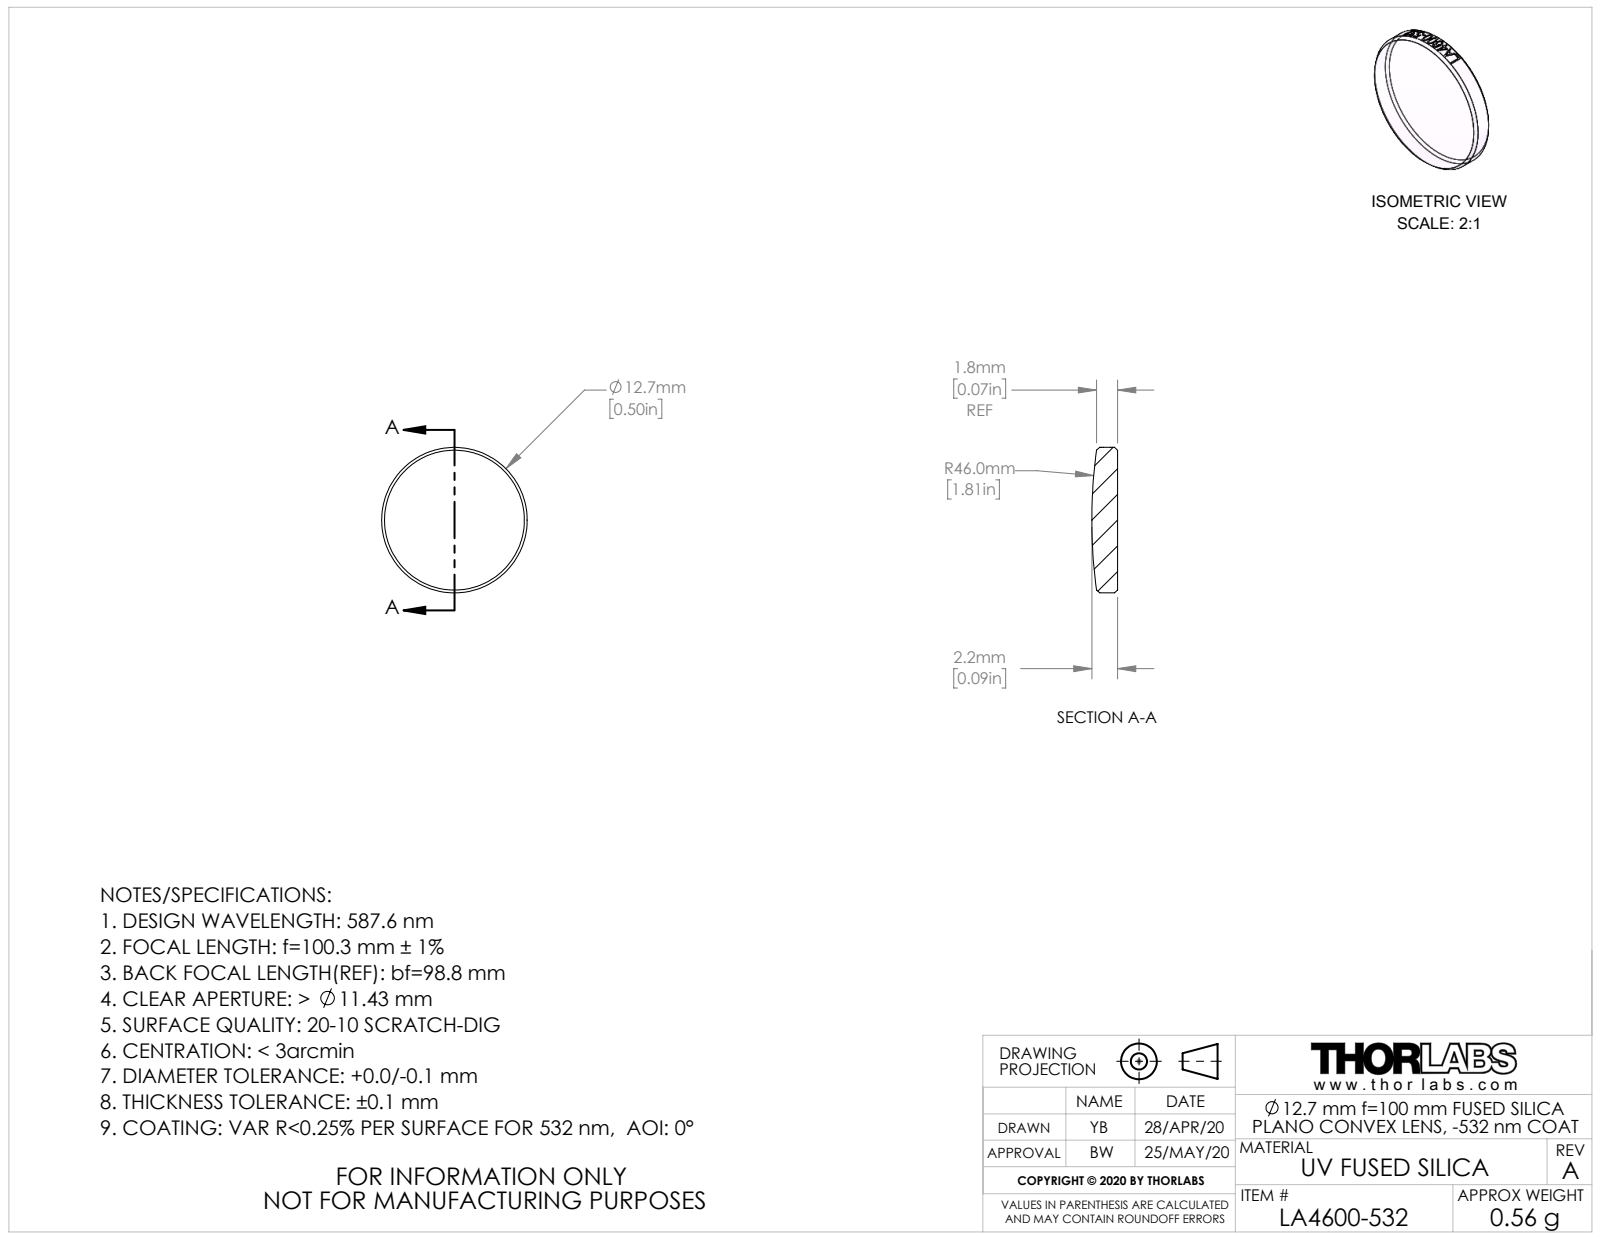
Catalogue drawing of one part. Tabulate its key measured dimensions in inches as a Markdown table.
| quantity | value |
| --- | --- |
| part name | CTN015726-E0W |
| STEP written by | SolidWorks 2018 (AUTOMOTIVE_DESIGN) |
| units | inches |
| bodies | 1 solid, 24 faces (1 planar, 17 cylindrical, 6 other) |
| overall size | 0.5 × 0.5 × 0.088 |
| volume | 0.015 in³ |
| surface area | 0.488 in² |
| round bosses / shafts (diameter × count) | 0.5 × 1 |
